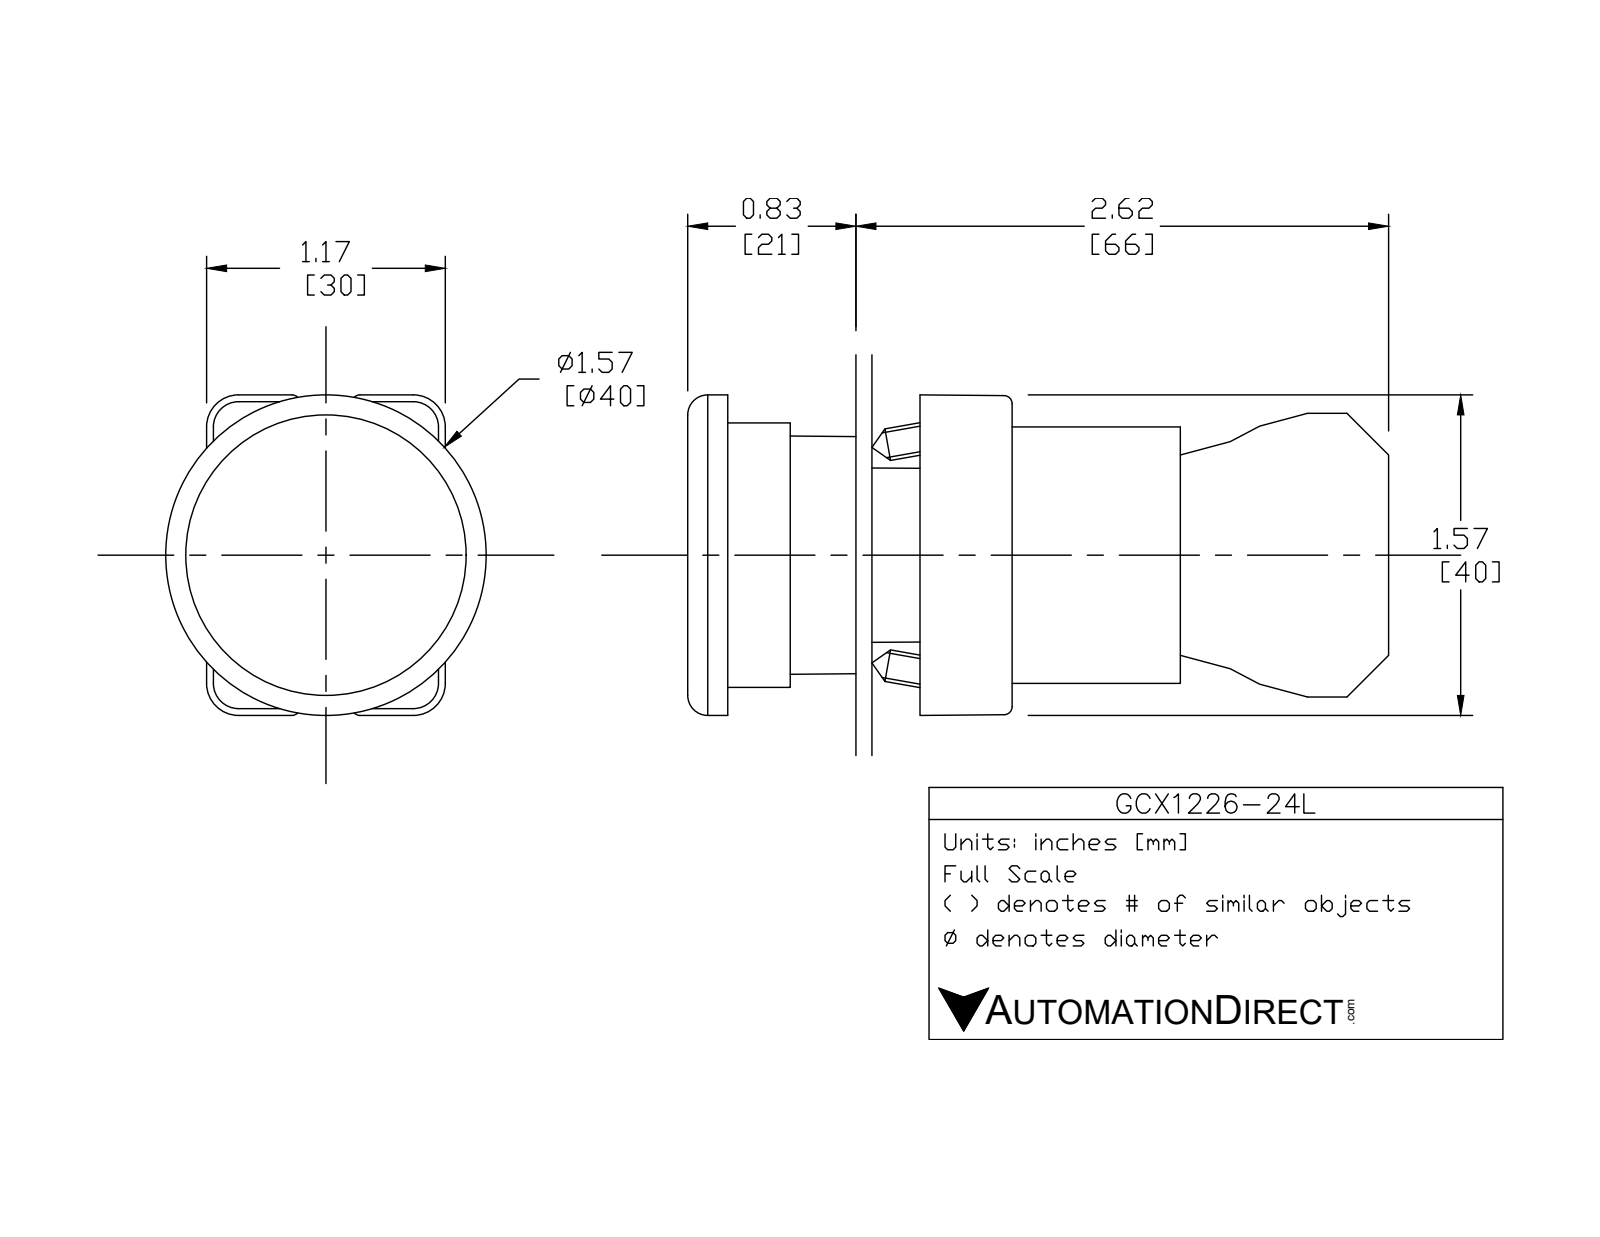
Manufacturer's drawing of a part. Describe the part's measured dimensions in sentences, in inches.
The part is named "ecx1030; GCX1226-24L; ECX1050; GCX122X OPERATOR (+1 more)". Its 3-D file was written by "SolidWorks 2016 (AUTOMOTIVE_DESIGN)". It is 7 solids with 431 faces: 252 planar, 146 cylindrical and 33 other. Overall it measures 3.469 by 1.581 by 1.575 inches. Its volume is 2.895 cubic inches and its surface area 40.89 square inches. Round holes: 2 of diameter 0.079, 2 of diameter 0.124, 2 of diameter 0.13, 1 of diameter 0.087, 1 of diameter 0.197, 1 of diameter 0.469, 1 of diameter 0.878, 1 of diameter 0.888, 1 of diameter 1.024, 1 of diameter 1.181. Round bosses or shafts: 4 of diameter 0.157, 1 of diameter 1.299, 1 of diameter 1.175, 1 of diameter 0.945, 1 of diameter 0.856, 1 of diameter 0.78, 1 of diameter 0.504. Partial cylindrical surfaces (rounded edges, fillets, slot ends): 24 of radius 0.059, 12 of radius 0.041, 12 of radius 0.124, 12 of radius 0.157, 8 of radius 0.039, 2 of radius 0.128, 1 of radius 0.02, 1 of radius 0.063. The main face-to-face distances are 0.827, 2.445, 1.618, 0.579, 2.287, 1.461, 0.157, 0.587, 0.031, 1.165. The hole center spacings are 0.236, 0.539, 0.472, 0.484.
